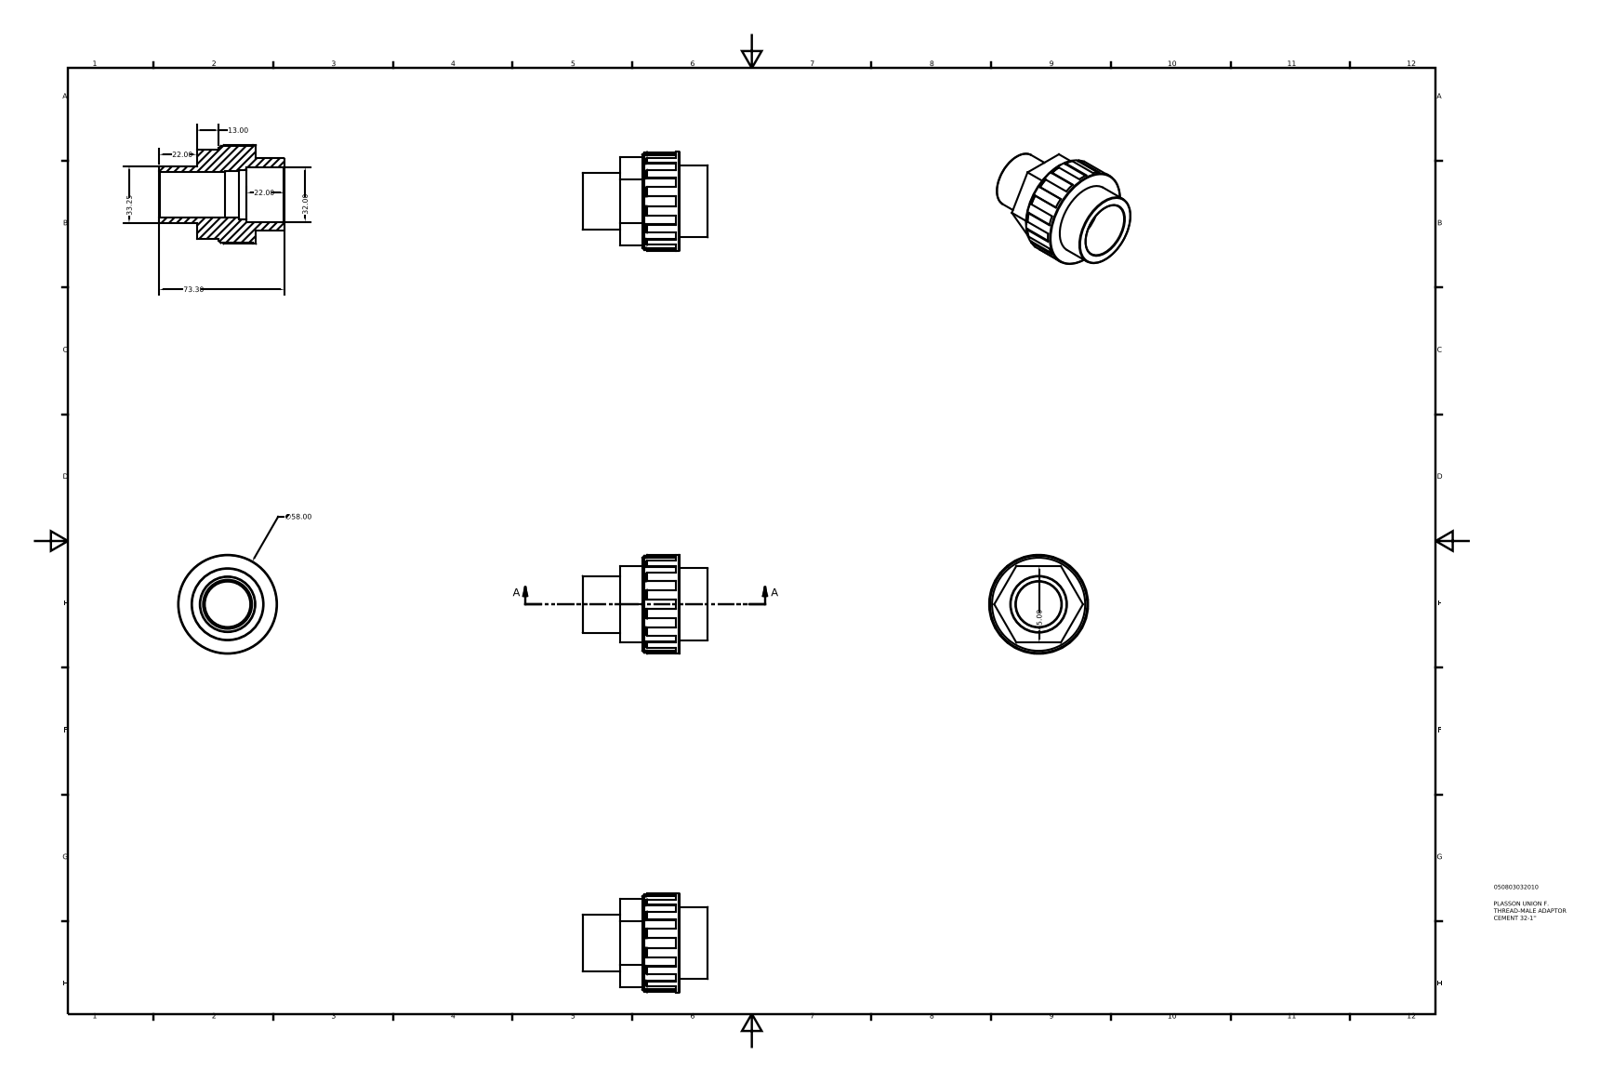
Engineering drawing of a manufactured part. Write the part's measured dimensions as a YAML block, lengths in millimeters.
part_name: "050803032010"
step_written_by: "Autodesk Inventor 2015 (AUTOMOTIVE_DESIGN)"
units: millimeters
bodies: {solids: 1, faces: 92, planar: 62, cylindrical: 8, other: 22}
overall_size: [73.3, 58, 58]
volume: 74466
surface_area: 21249
round_holes:
  - {diameter: 26.6, count: 1}
  - {diameter: 27.2, count: 1}
  - {diameter: 28.8, count: 1}
  - {diameter: 32, count: 1}
round_bosses_or_shafts:
  - {diameter: 58, count: 1}
  - {diameter: 56.84, count: 1}
  - {diameter: 42.24, count: 1}
  - {diameter: 33.25, count: 1}
face_to_face_distances: [45, 34.8, 51.3, 13, 21.8, 16.5, 38.3, 22, 35, 56.8]
